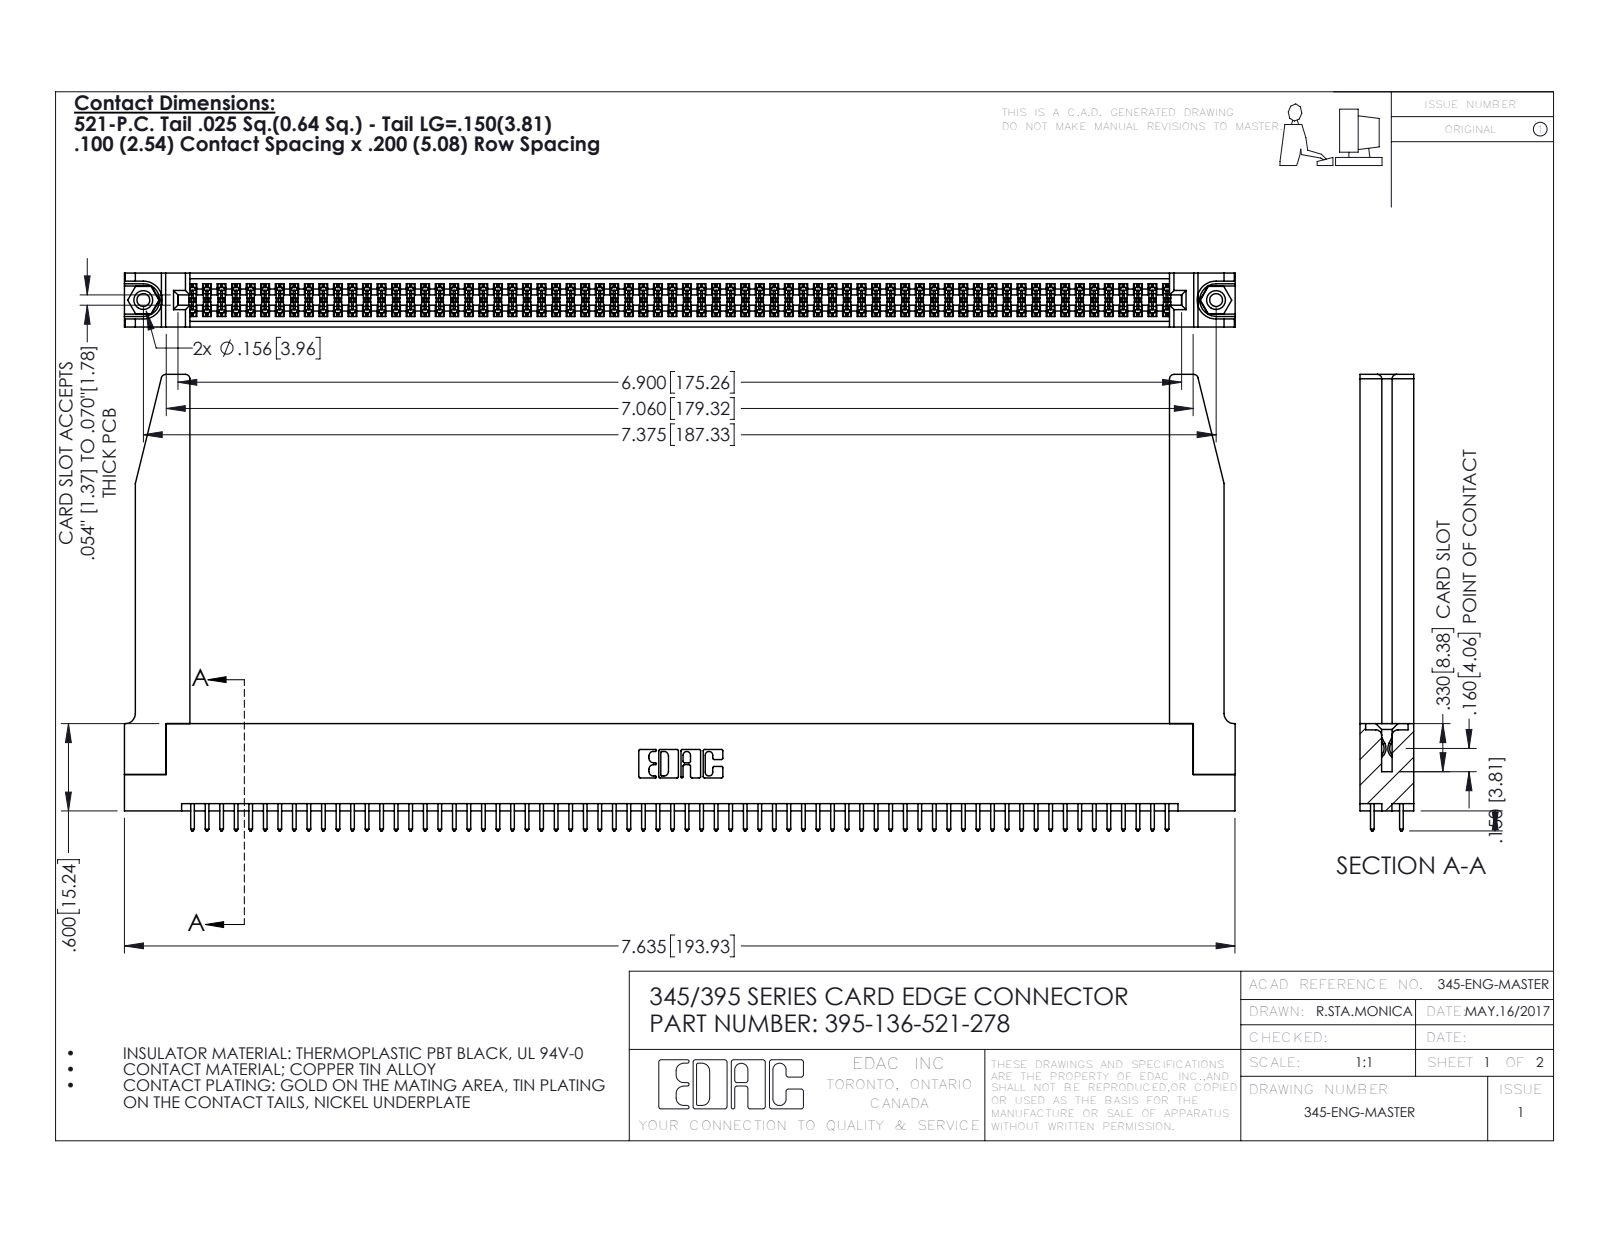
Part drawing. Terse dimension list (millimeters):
name: 395-136-521-278; 345-220-078_345-220-078; 345-292-001_345-293-121; 345 Part_Flush Mounting Lugs - 0.156 Dia-TH (+1 more)
written by: SolidWorks 2016 (CONFIG_CONTROL_DESIGN)
unit: mm
bodies: 141 solids, 7160 faces (4710 planar, 2398 cylindrical, 52 other)
size: 194 × 79.7 × 9.4
volume: 26 790 mm³; area: 35 100 mm²
holes: 2× ⌀2.3, 2× ⌀3.2, 2× ⌀4, 1× ⌀1.6
bosses: 2× ⌀3.9
rounds: 204× R0.2, 136× R0.3, 22× R0.3, 8× R0.8, 6× R0.2, 6× R0.8, 3× R0.7, 2× R0.4
face distances: 1.8, 7.6, 9.4, 5.1, 2.5, 6.9, 0.6, 5.7, 4.4, 3.8
hole spacings: 6.9, 181.3, 187.3
